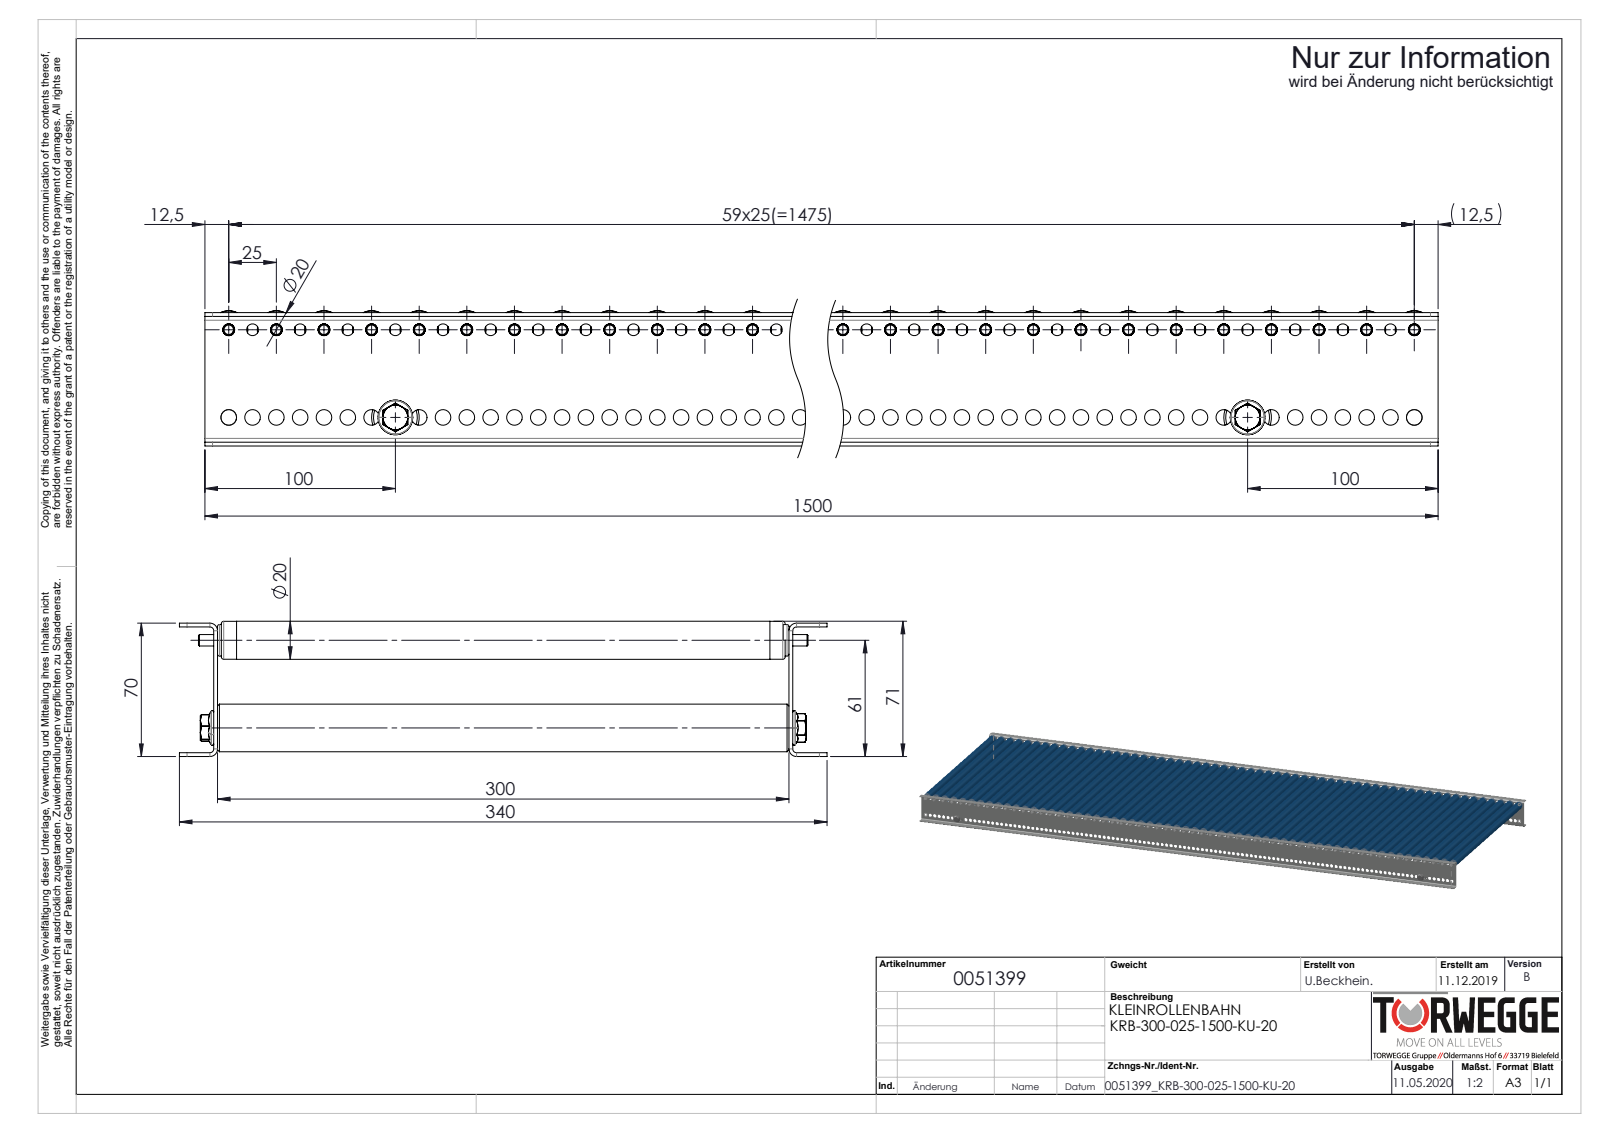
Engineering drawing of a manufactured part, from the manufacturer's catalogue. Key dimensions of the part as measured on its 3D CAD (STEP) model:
Part name (STEP PRODUCT): 0039777_Achse-Ø06-FA-KFG_L=320 fr D20; KUT50-20x1,5-KU-A6_FA-EL=KFG_L=300; Traversen_KFG_L300; 0051399 (+4 more)
STEP written by: SolidWorks 2020 (AUTOMOTIVE_DESIGN)
Units: millimetres
Bodies: 372 solids, 15860 faces (5272 planar, 5916 cylindrical, 4672 other)
Overall size (bounding box): 1500 × 340 × 71
Volume: 3 310 000 mm³ · Surface area: 3 519 000 mm²
Round holes (diameter × count): ⌀6.2 ×119, ⌀8.2 ×119, ⌀6.1 ×60, ⌀12.4 ×60, ⌀13.2 ×60, ⌀14.6 ×60, ⌀16.2 ×60, ⌀17 ×60, ⌀17.2 ×60, ⌀6.8 ×2
Round bosses / shafts (diameter × count): ⌀20 ×60, ⌀19.9 ×60, ⌀17.1 ×60, ⌀16.8 ×60, ⌀16.5 ×60, ⌀11.4 ×60, ⌀11.1 ×60, ⌀10.2 ×60
Partial cylindrical surfaces — rounded edges, fillets, slot ends (radius × count): R4.05 ×60, R4 ×8, R2 ×4
Main face-to-face distances: 2, 302, 68, 300, 304, 70, 66, 292, 10, 12
Hole centre spacings: 12.5, 25, 37.5, 50, 62.5, 75, 87.5, 100
